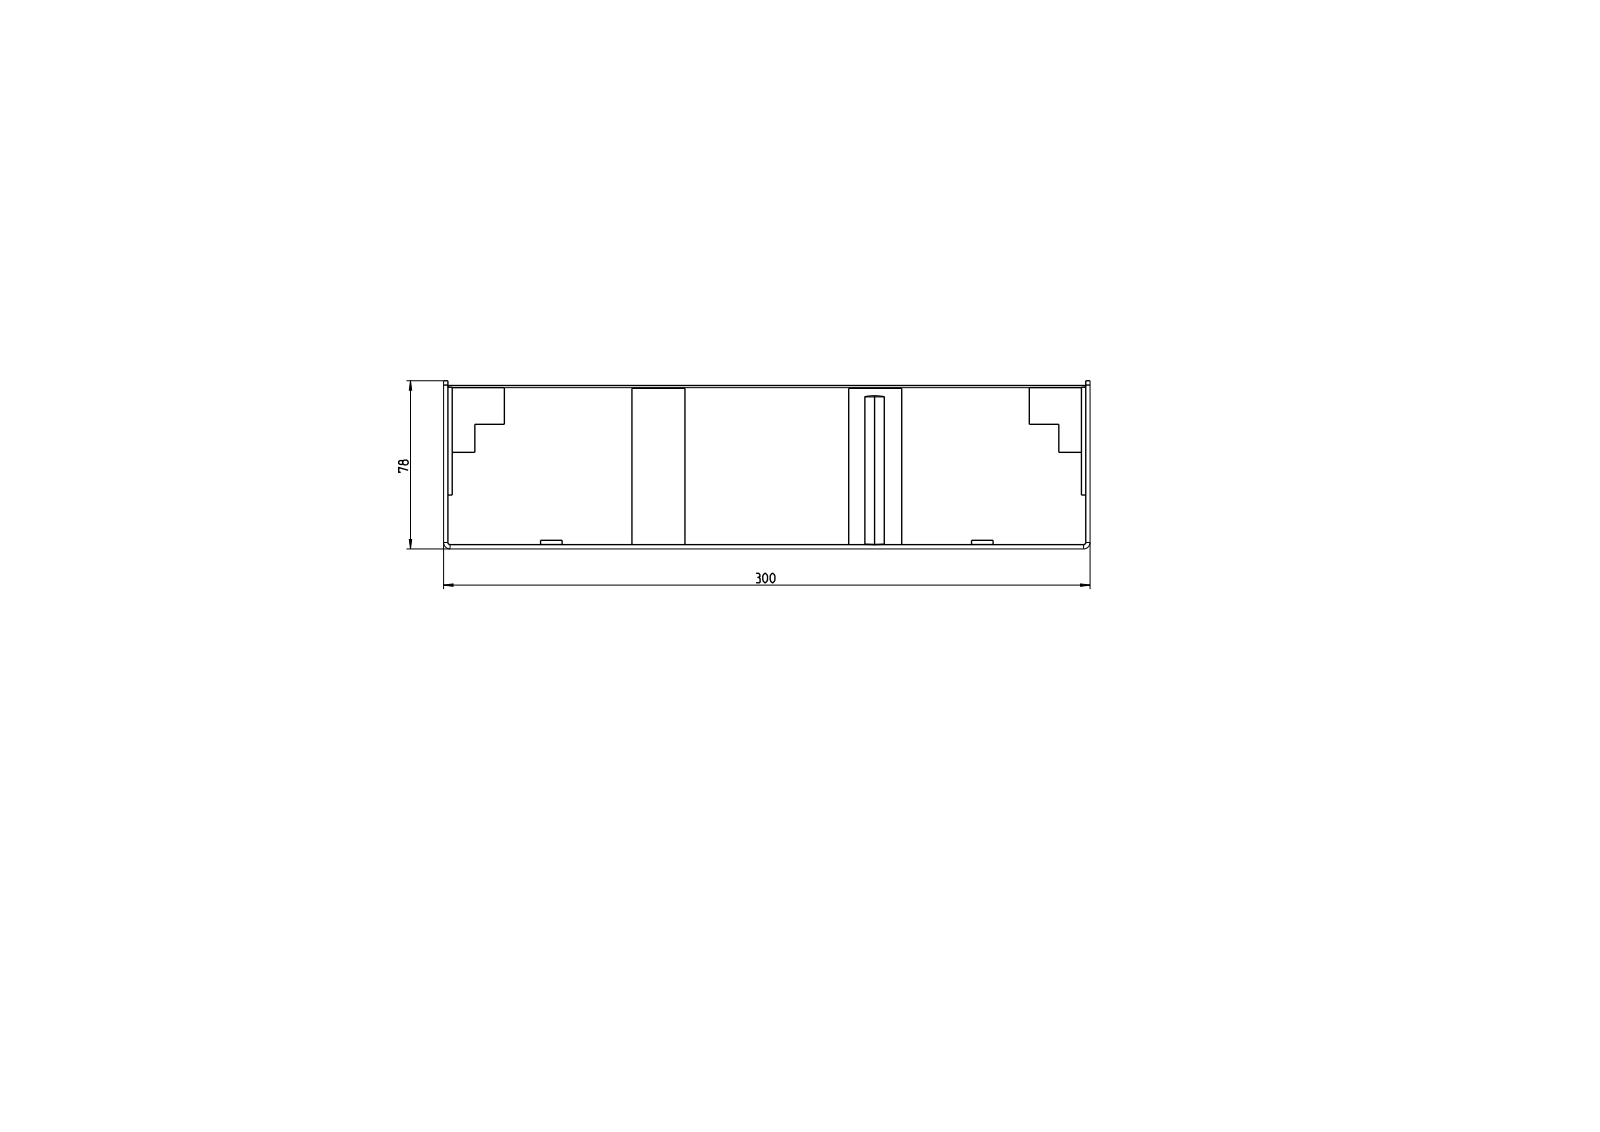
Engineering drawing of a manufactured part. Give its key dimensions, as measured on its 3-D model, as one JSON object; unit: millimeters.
{"part_name": "T-01021; T-01024; T-01025_AF0; T-01026_ASM (+8 more)", "step_written_by": "CREO PARAMETRIC BY PTC INC, 2022024 (AUTOMOTIVE_DESIGN)", "units": "millimeters", "bodies": {"solids": 17, "faces": 542, "planar": 388, "cylindrical": 102, "other": 52}, "overall_size": [2000, 300, 78.23], "volume_mm3": 9518000, "surface_area_mm2": 4689000, "round_holes": [[13.6, 10], [6, 8], [8.5, 8]], "round_bosses_or_shafts": [[10, 8]], "partial_cylinders_radius": [[0.1, 20], [1, 2], [3, 2]], "face_to_face_distances": [2, 72.8, 73.8, 1, 74.8, 75.8, 296, 294, 4, 298], "hole_center_spacings": [600, 632.46, 1200, 20, 200, 201, 1216.55, 580]}
